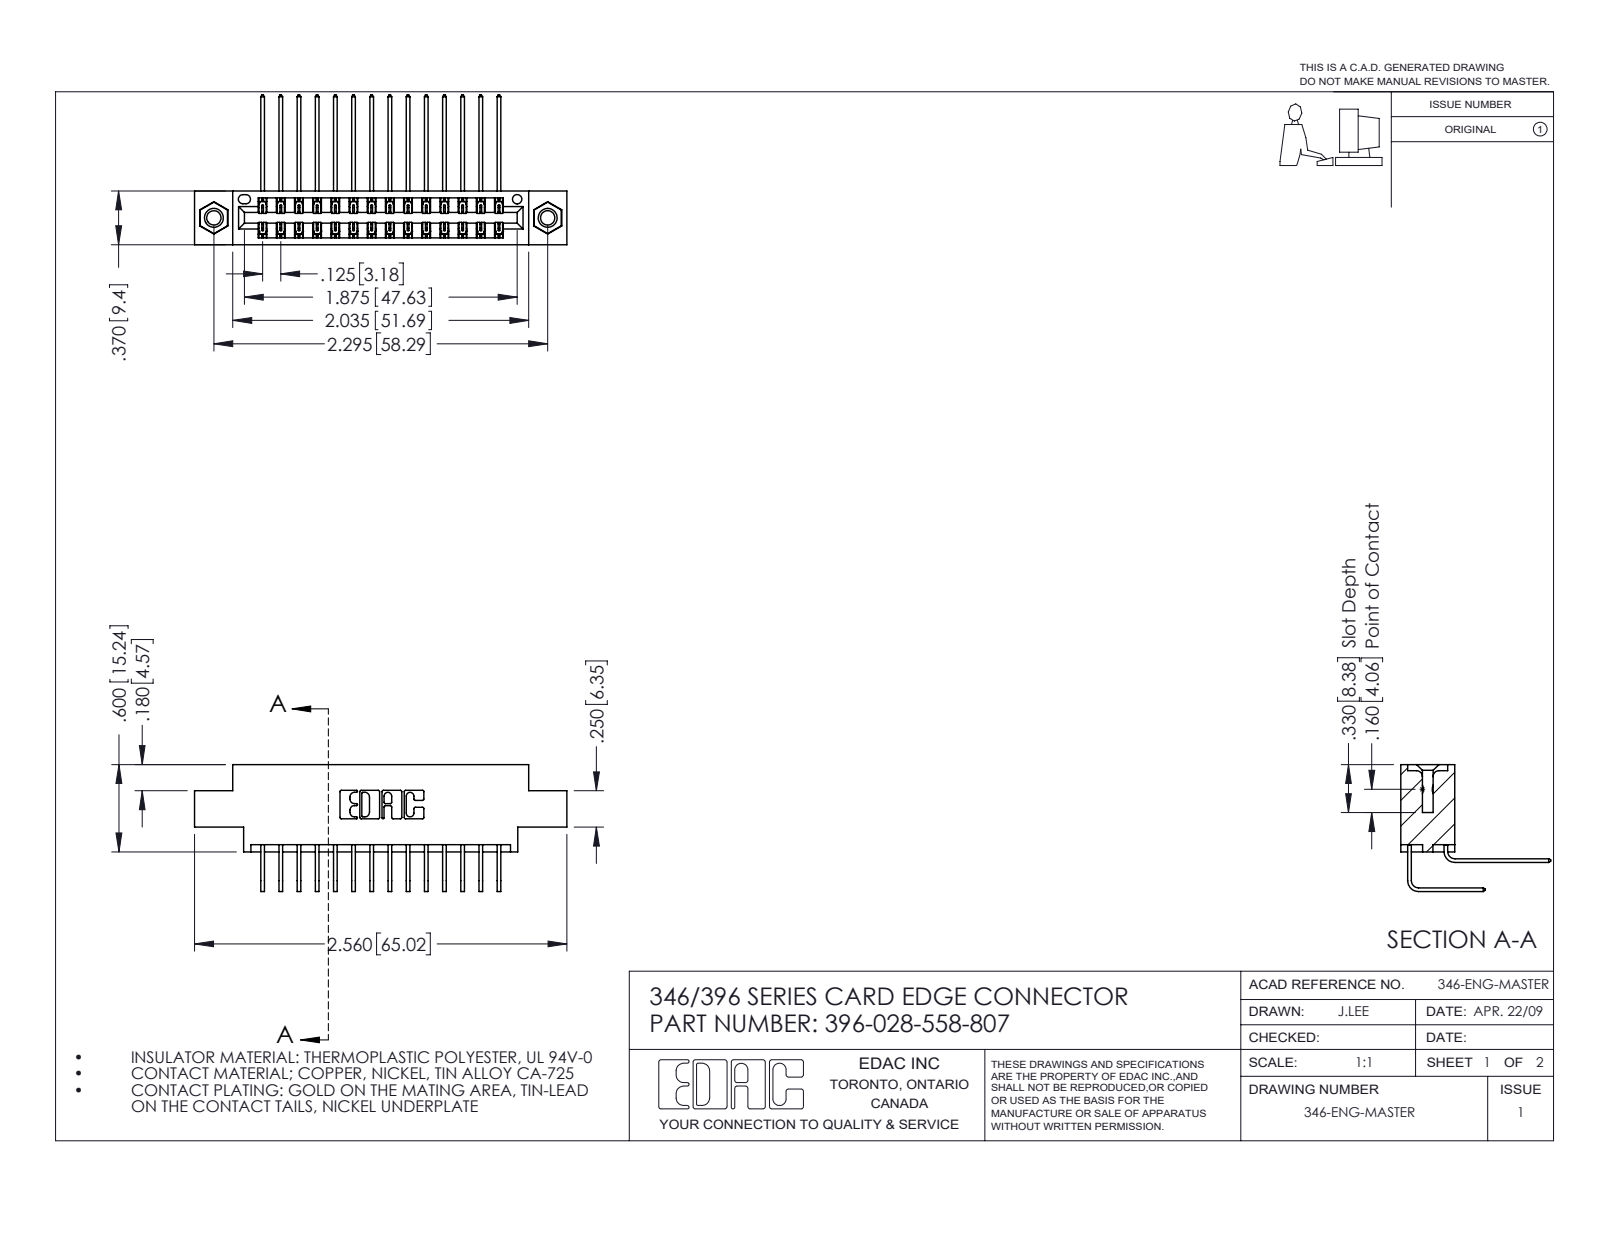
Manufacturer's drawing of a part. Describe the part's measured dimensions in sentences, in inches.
The part is named "345-250-001_345-250-005-103; 345-292-001_558 559 Tail - 1; 346 Part_0.170 Offset - 0.156 Dia-TI; 345-292-001_558 Tail - 2 (+1 more)". Its 3-D file was written by "SolidWorks 2016 (CONFIG_CONTROL_DESIGN)". It is 31 solids with 1698 faces: 1148 planar, 534 cylindrical and 16 other. Overall it measures 2.56 by 1.03 by 0.873 inches. Its volume is 0.373 cubic inches and its surface area 13.88 square inches. Round holes: 2 of diameter 0.098, 2 of diameter 0.125, 2 of diameter 0.156, 1 of diameter 0.064. Round bosses or shafts: 2 of diameter 0.155. Partial cylindrical surfaces (rounded edges, fillets, slot ends): 42 of radius 0.006, 22 of radius 0.01, 6 of radius 0.007, 6 of radius 0.031, 3 of radius 0.026, 2 of radius 0.014, 2 of radius 0.022, 2 of radius 0.024. The main face-to-face distances are 0.048, 0.322, 0.37, 0.25, 0.025, 0.072, 0.298, 0.222, 0.275, 0.148. The hole center spacings are 0.246, 2.089, 2.295.
